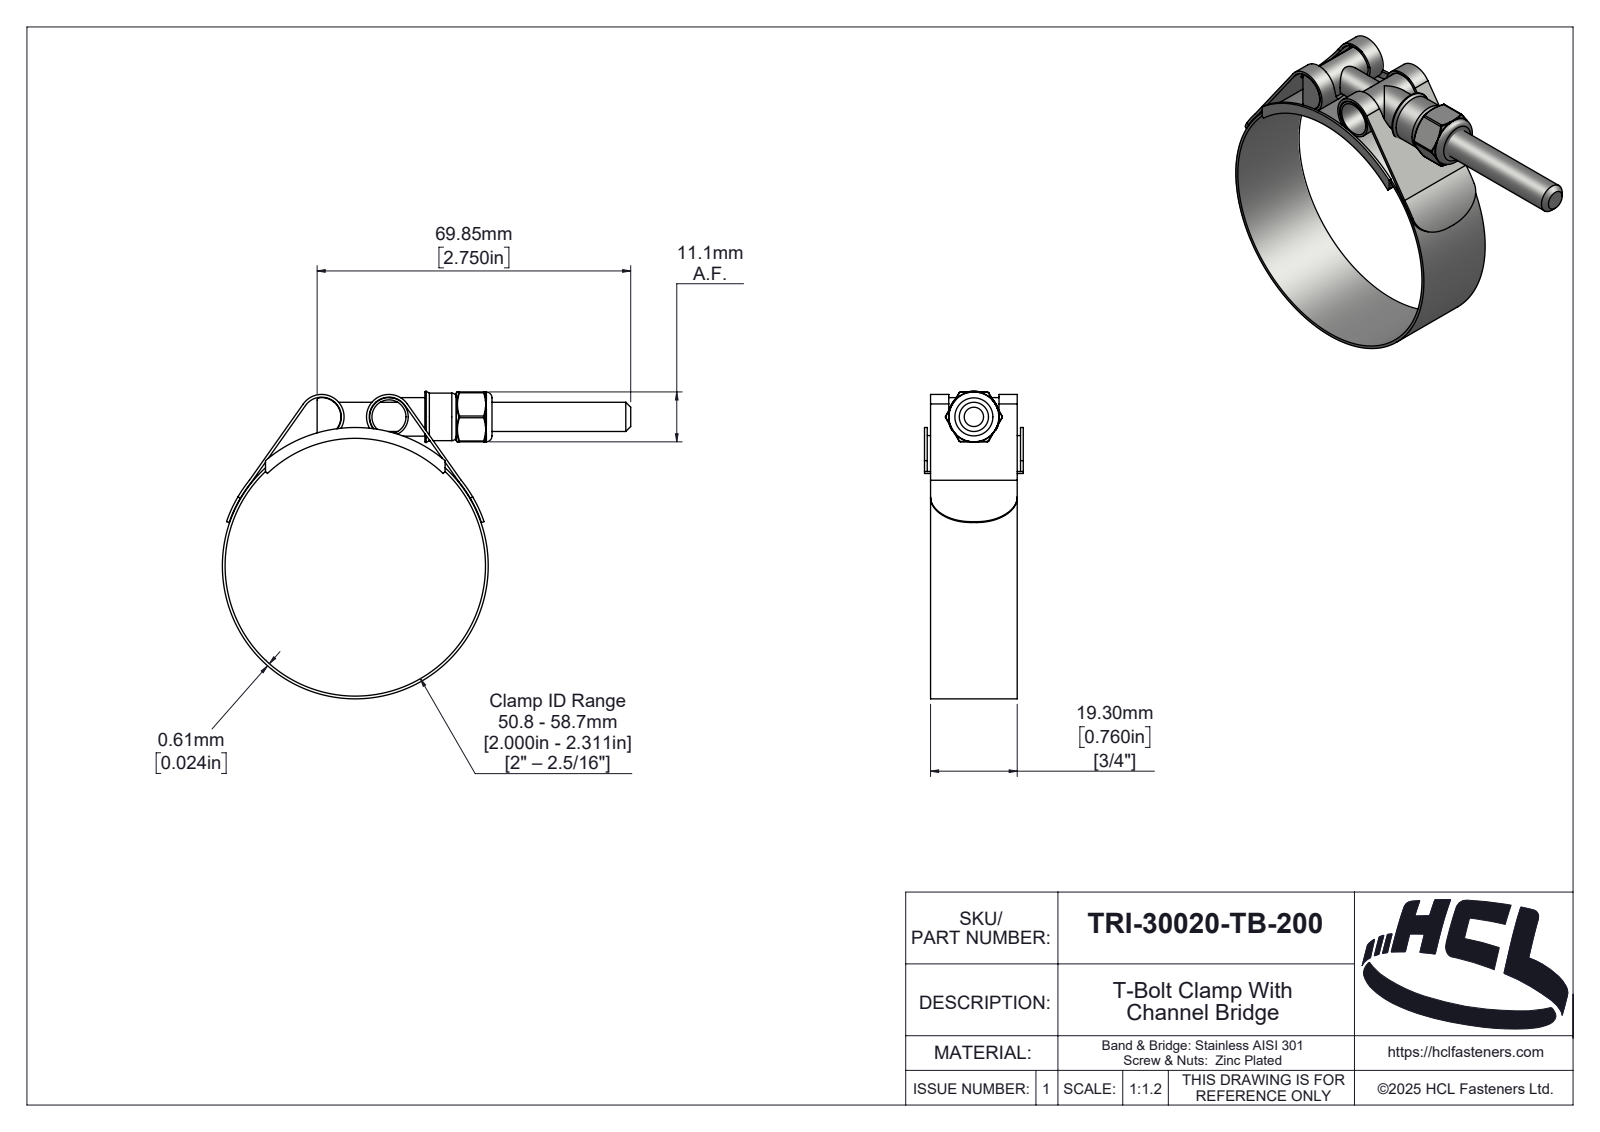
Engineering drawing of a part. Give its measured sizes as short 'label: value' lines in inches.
name: TRI-30020-TB-200
written by: SolidWorks 2025 (AUTOMOTIVE_DESIGN)
unit: in
bodies: 6 solids, 334 faces (44 planar, 126 cylindrical, 164 other)
size: 3.581 × 2.696 × 0.866
volume: 0.469 in³; area: 25.33 in²
holes: 1× ⌀0.213, 1× ⌀0.25, 1× ⌀0.256, 1× ⌀0.298, 1× ⌀2.283
bosses: 2× ⌀0.338, 1× ⌀2.331, 1× ⌀0.417
rounds: 6× R0.015, 2× R0.02, 2× R0.173, 2× R0.197, 2× R0.22, 1× R0.023, 1× R0.095, 1× R0.119
face distances: 0.024, 0.029, 0.053, 0.813, 0.76, 0.842, 0.789, 0.437, 0.866, 0.818
hole spacings: 1.339
